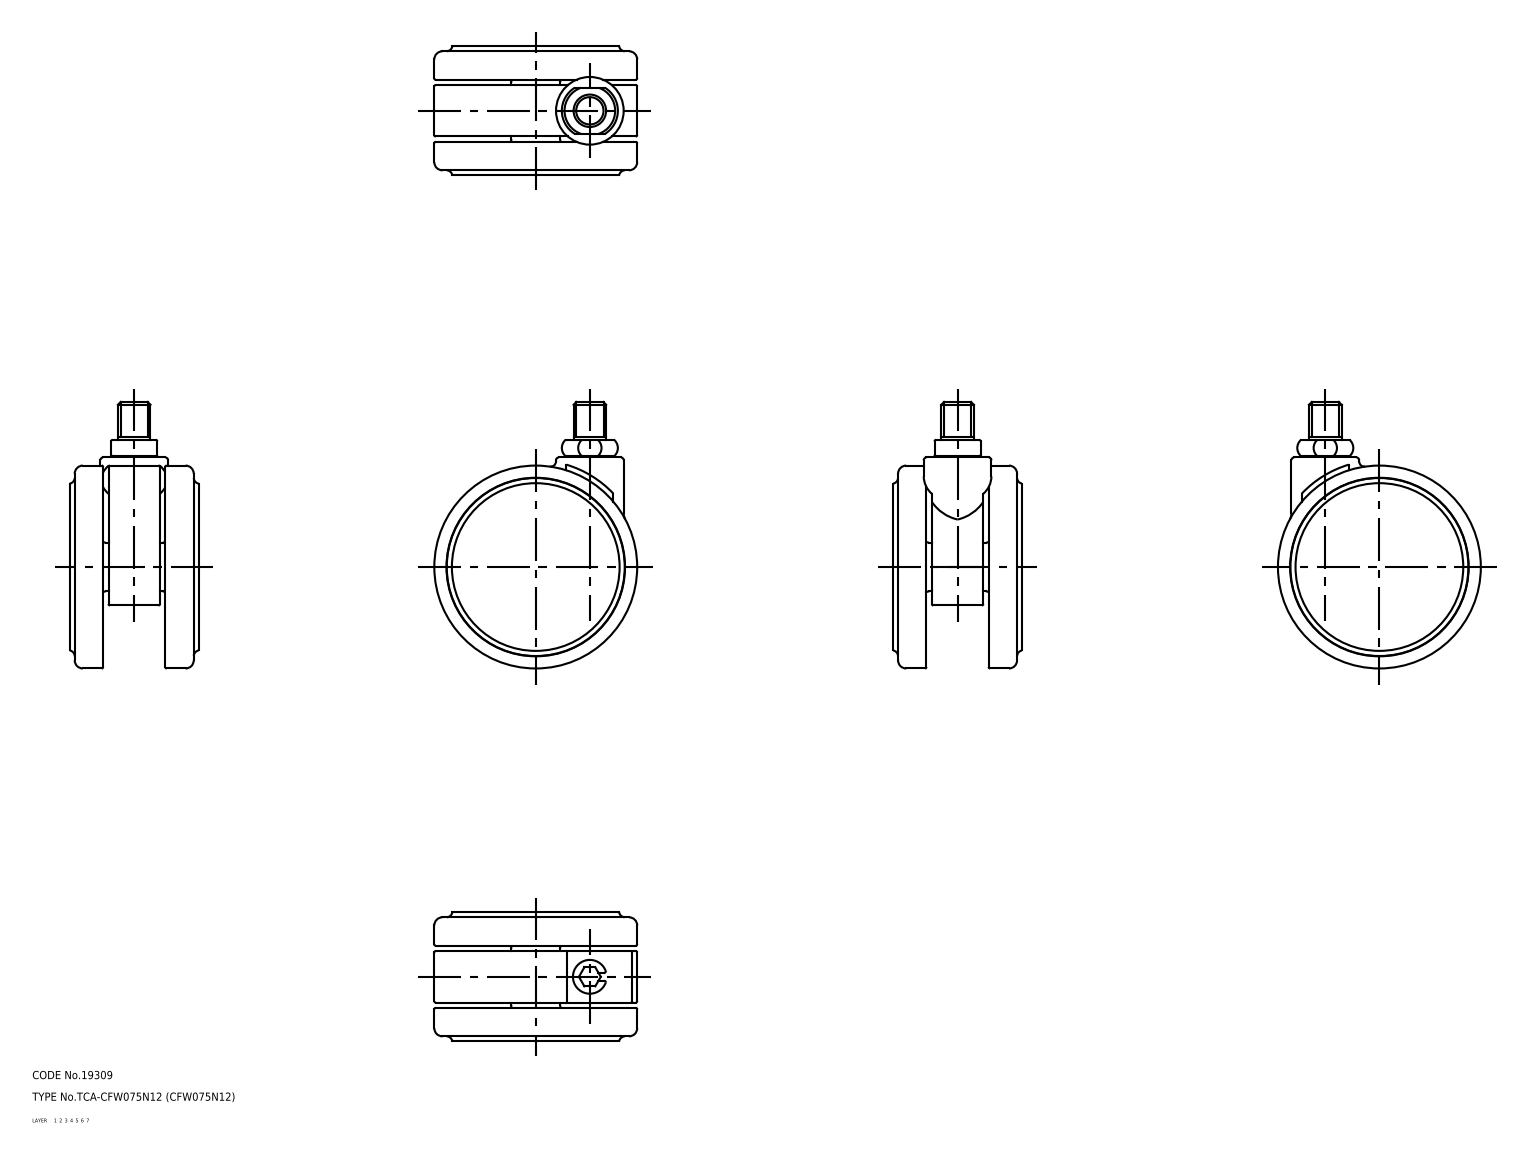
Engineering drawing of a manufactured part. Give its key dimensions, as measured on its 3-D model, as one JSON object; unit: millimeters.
{"part_name": "67118078; 67118091; 67118104; 67118117", "step_written_by": "CADfix (AUTOMOTIVE_DESIGN)", "units": "millimeters", "bodies": {"solids": 4, "faces": 129, "planar": 0, "cylindrical": 0, "other": 129}, "overall_size": [98.5, 75, 47.6], "volume_mm3": 159374, "surface_area_mm2": 36942}
